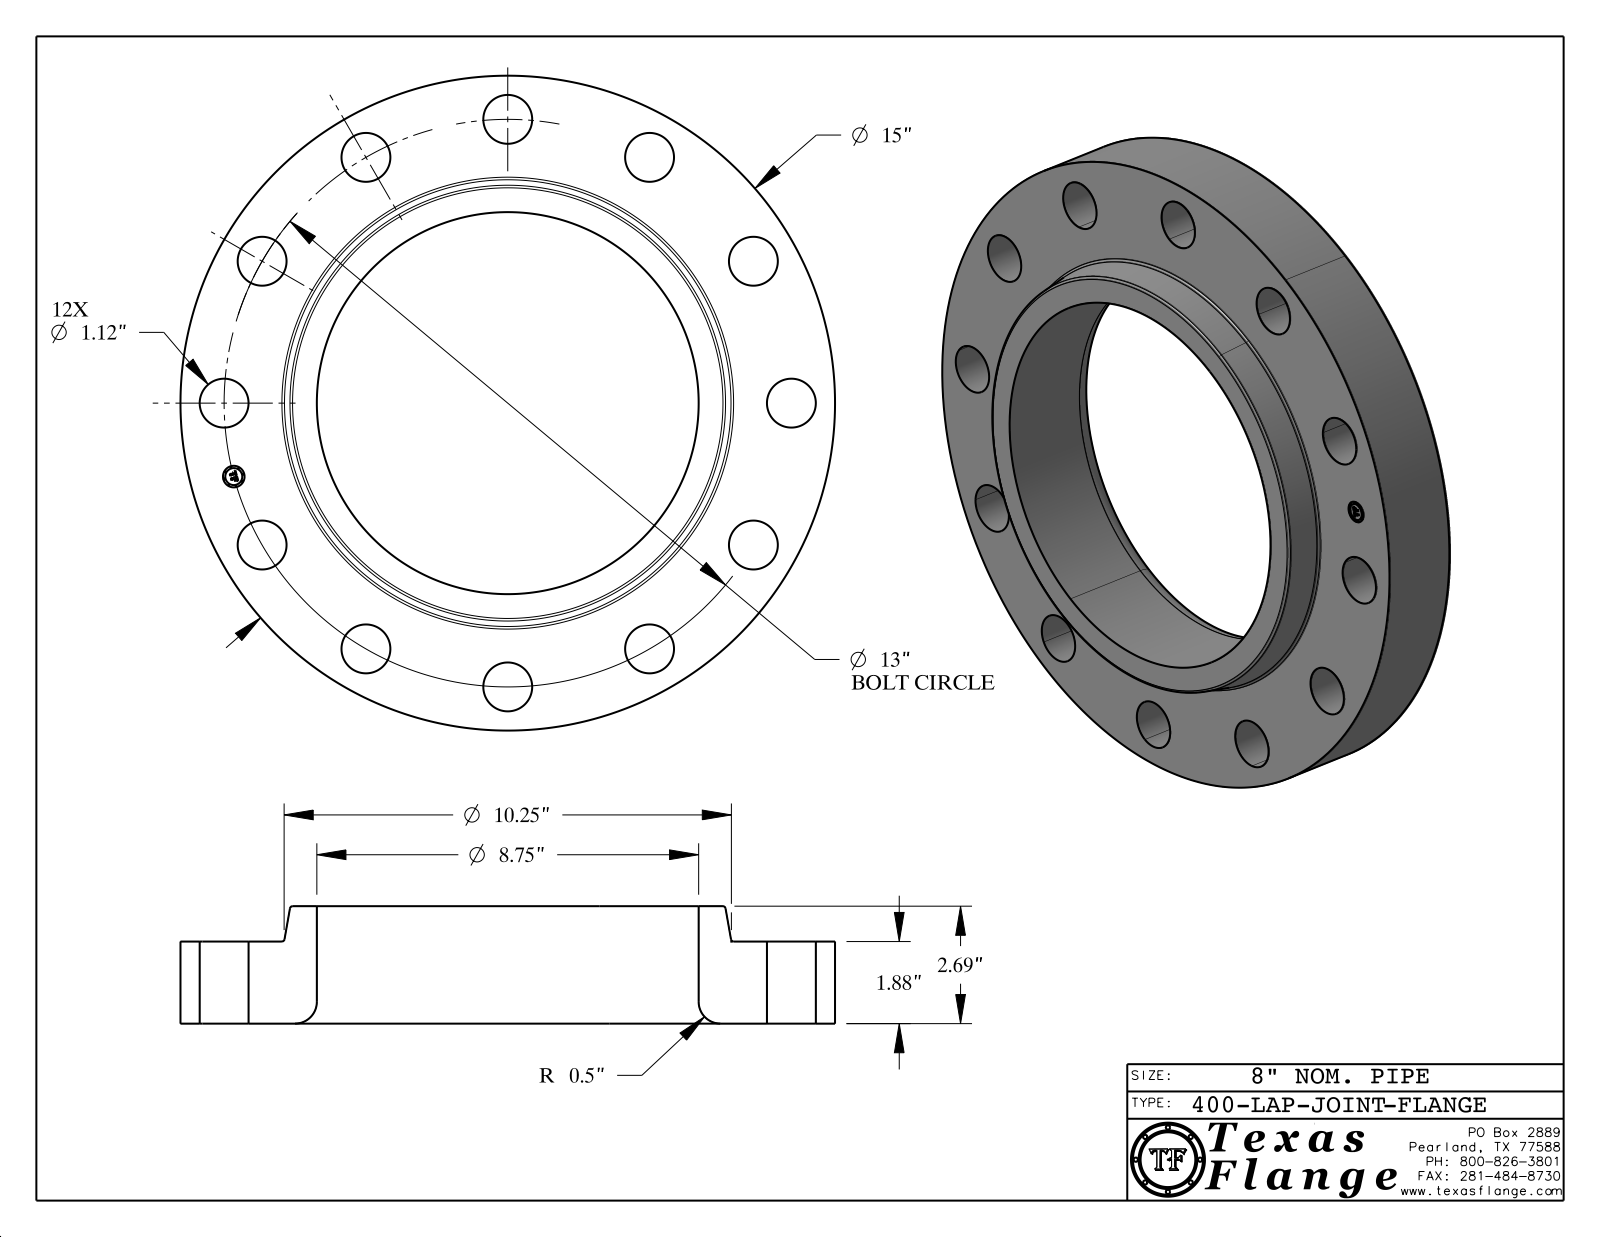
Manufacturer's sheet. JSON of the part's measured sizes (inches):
{"part_name": "400-LAP-JOINT FLANGE", "step_written_by": "CATIA V5 STEP AP214 (AUTOMOTIVE_DESIGN)", "units": "inches", "bodies": {"solids": 1, "faces": 424, "planar": 368, "cylindrical": 48, "other": 8}, "overall_size": [15, 15, 2.69], "volume_in3": 211.7, "surface_area_in2": 466.2, "round_holes": [[1.12, 12], [0.495, 1], [8.75, 1]], "round_bosses_or_shafts": [[0.03, 8], [15, 1], [0.39, 1]], "face_to_face_distances": [1.88, 2.69, 0.81, 1.865, 0.015, 0.825, 0.148, 0.144, 0.027, 0.096], "hole_center_spacings": [6.5, 3.365, 9.193, 11.258, 12.557, 13, 1.697, 4.975]}
